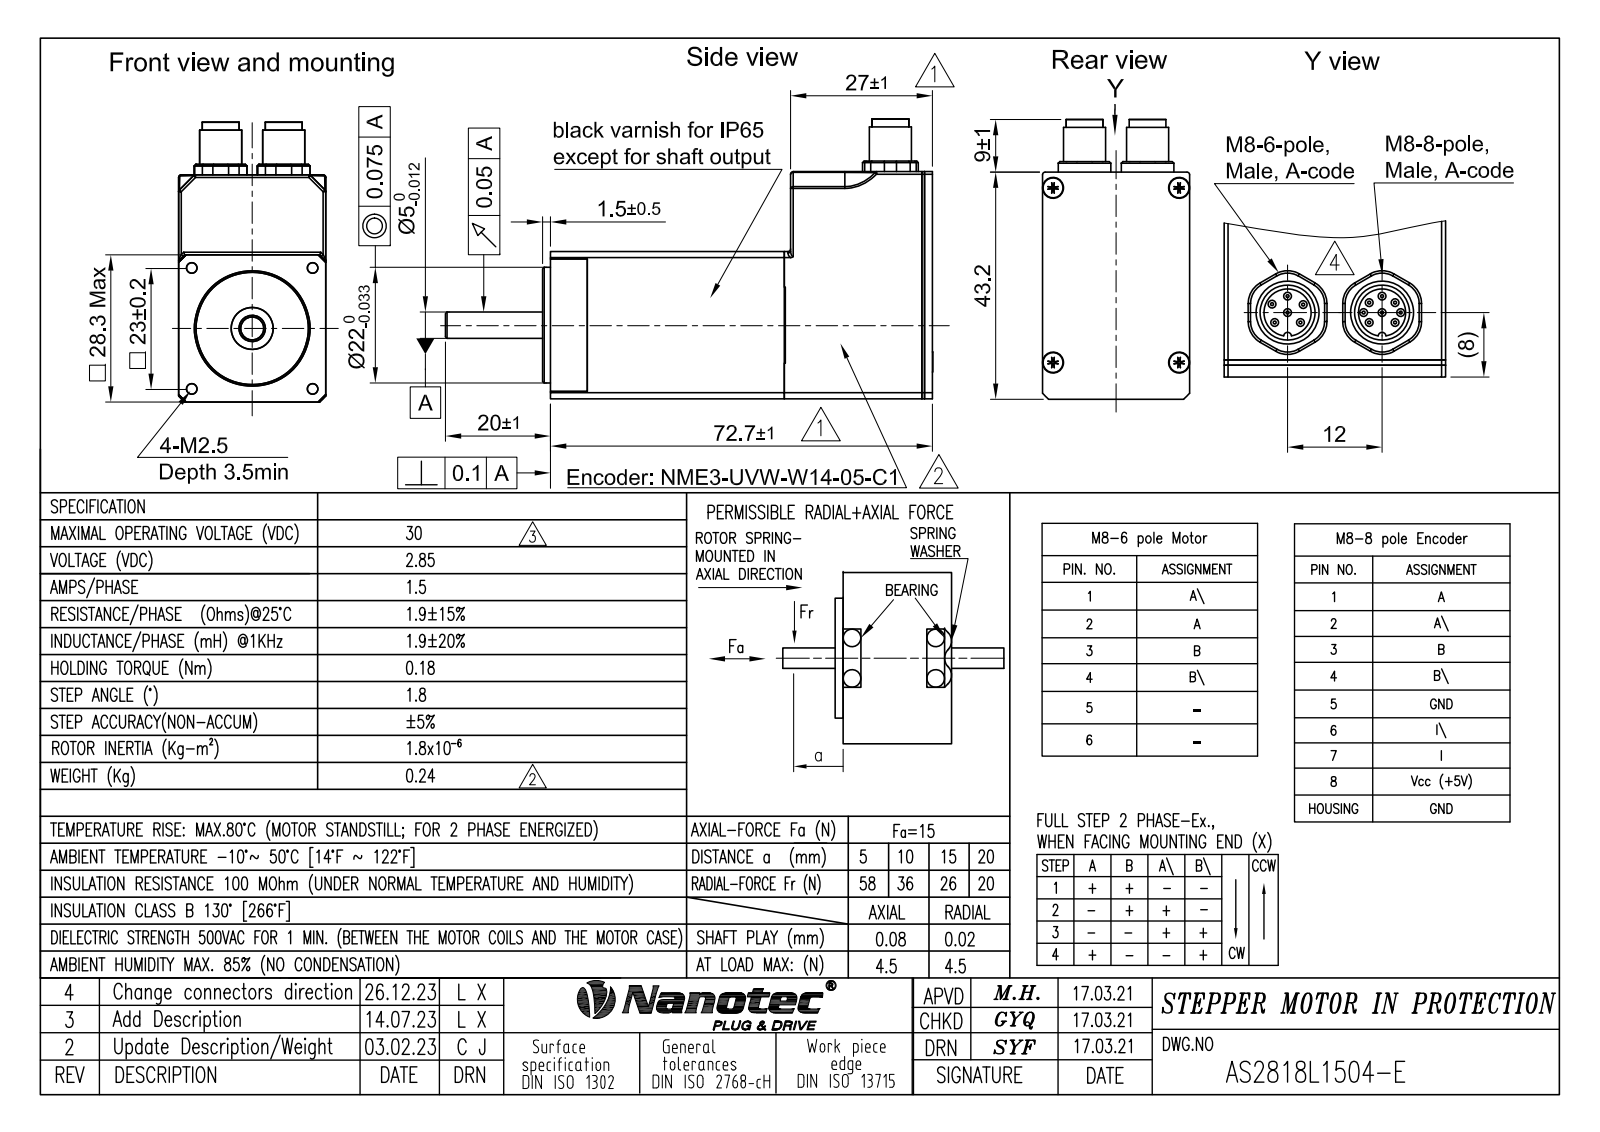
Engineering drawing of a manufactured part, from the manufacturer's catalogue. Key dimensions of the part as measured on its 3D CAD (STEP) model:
Part name (STEP PRODUCT): AS2818L1504-EB; NME3-14.5; NME3_SSI_W001_04_1; 底板1 (+8 more)
STEP written by: Autodesk Inventor 2020 (AUTOMOTIVE_DESIGN)
Units: millimetres
Bodies: 81 solids, 3774 faces (2957 planar, 529 cylindrical, 288 other)
Overall size (bounding box): 92.27 × 53.2 × 28
Volume: 51 763 mm³ · Surface area: 31 926 mm²
Round holes (diameter × count): ⌀1.57 ×4, ⌀1.8 ×4, ⌀2.01 ×4, ⌀2.17 ×4, ⌀2.8 ×4, ⌀4 ×4, ⌀6 ×3, ⌀0.4 ×2, ⌀0.5 ×2, ⌀1.22 ×2, ⌀2.2 ×2, ⌀2.4 ×2
Round bosses / shafts (diameter × count): ⌀3.8 ×8, ⌀2.5 ×4, ⌀2.21 ×4, ⌀2 ×4, ⌀1.74 ×4, ⌀8 ×2, ⌀7 ×2, ⌀3 ×2
Partial cylindrical surfaces — rounded edges, fillets, slot ends (radius × count): R0.5 ×47, R0.12 ×36, R0.1 ×29, R0.15 ×28, R0.3 ×28, R3 ×14, R2 ×10, R0.19 ×4
Main face-to-face distances: 28, 1.5, 26.5, 65.2, 16.25, 1, 18.25, 2.3, 62.9, 25
Hole centre spacings: 11.52, 12.26, 16.26, 22, 23, 25.09, 3.45, 3.55
